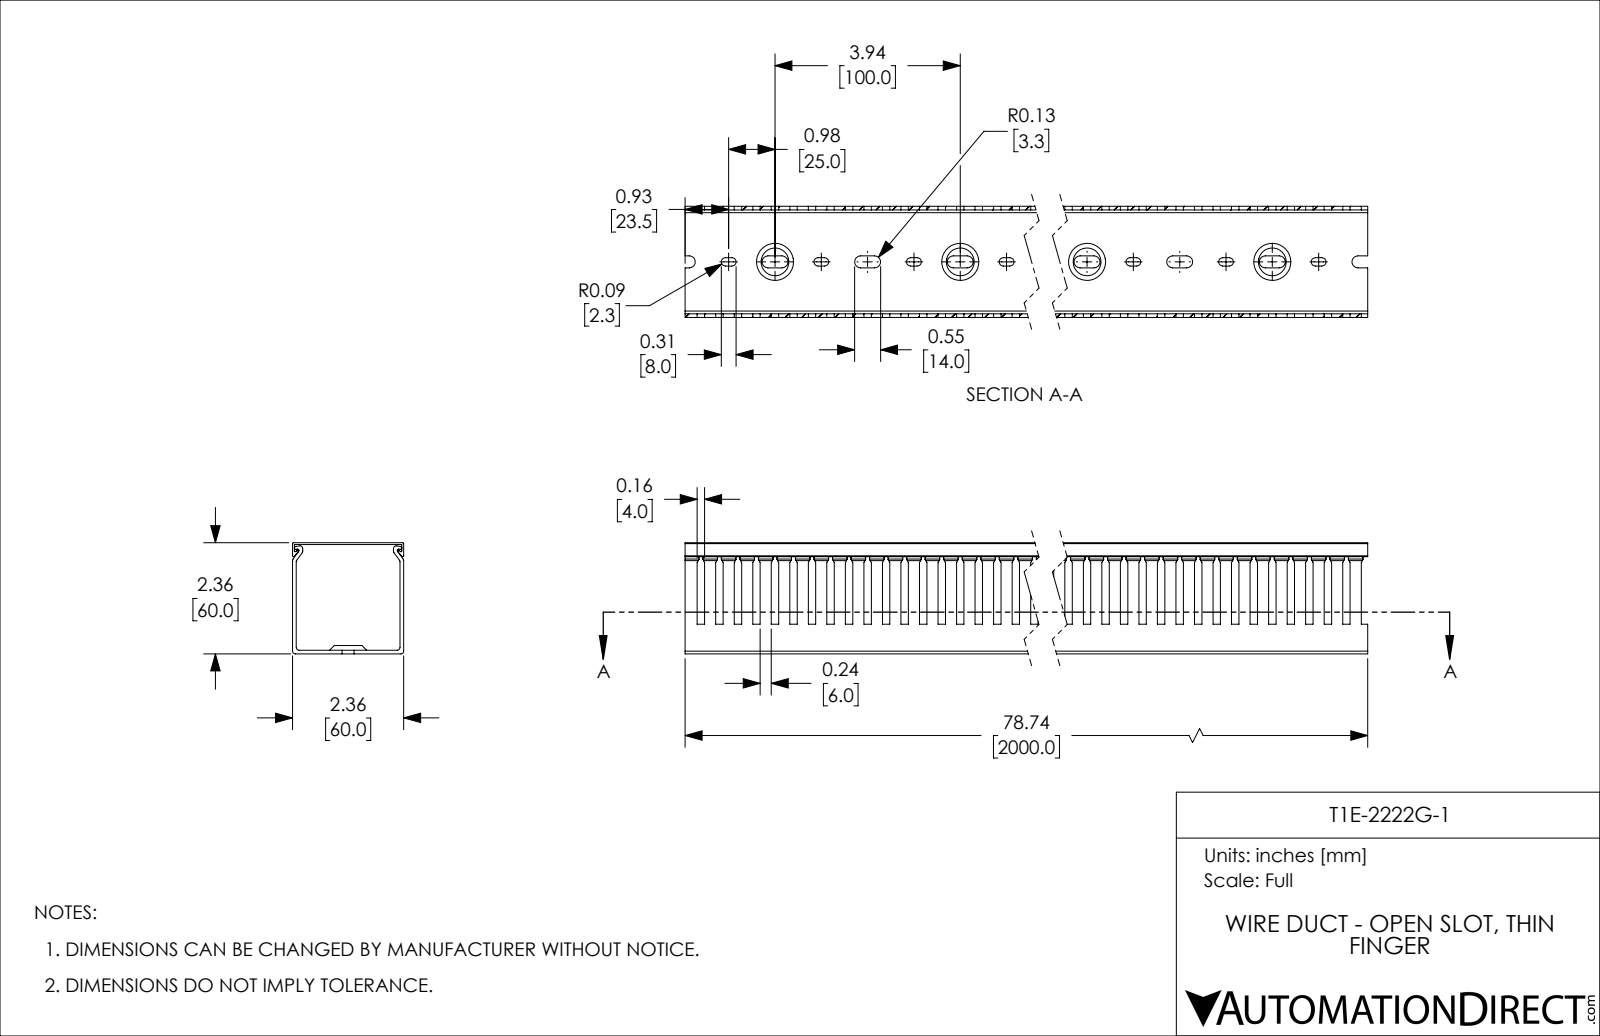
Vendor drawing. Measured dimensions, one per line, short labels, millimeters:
name: T1E-2222G-1
written by: SolidWorks 2021 (CONFIG_CONTROL_DESIGN)
unit: mm
bodies: 2 solids, 1005 faces (534 planar, 431 cylindrical, 40 other)
size: 2000 × 60 × 60
volume: 862 740 mm³; area: 1 019 000 mm²
rounds: 80× R2.25, 80× R3.25, 12× R1.5, 8× R0.5, 6× R0.75
face distances: 2, 58, 60, 1, 59, 57, 56, 4.5, 54.5, 5.5
